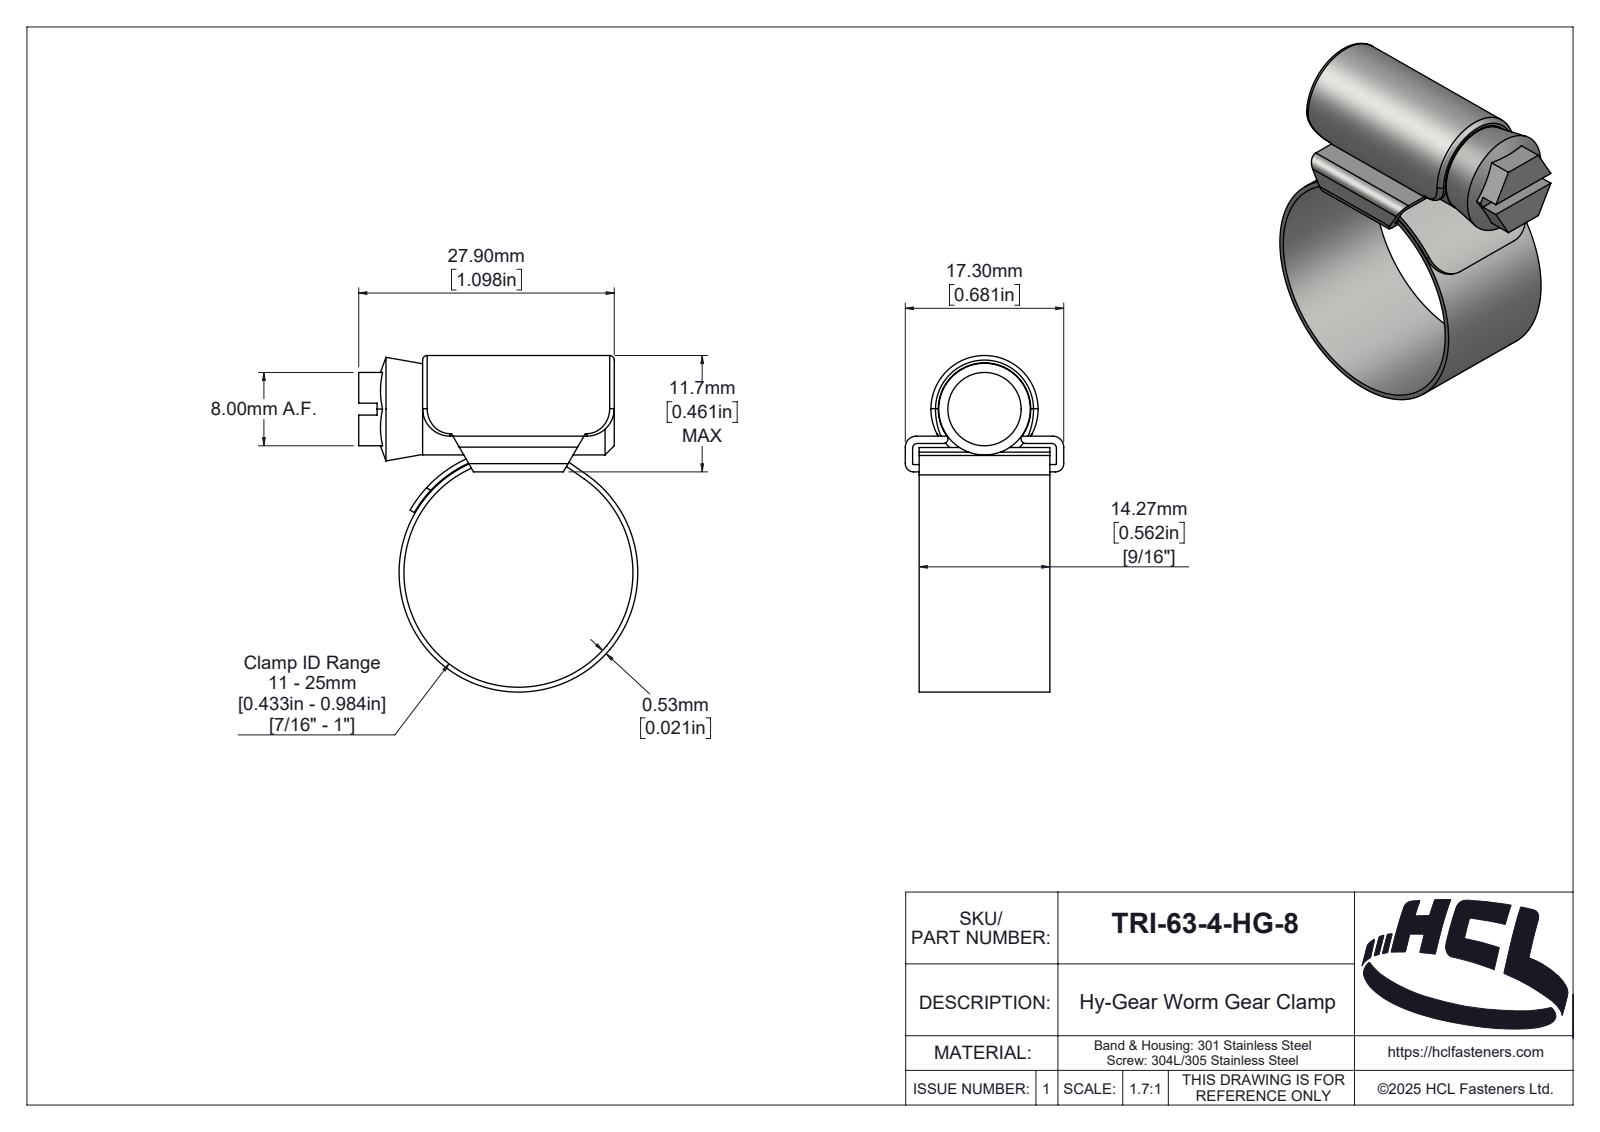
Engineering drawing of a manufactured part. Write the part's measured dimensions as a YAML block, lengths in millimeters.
part_name: "TRI-50-0-HG-8"
step_written_by: "SolidWorks 2025 (AUTOMOTIVE_DESIGN)"
units: millimeters
bodies: {solids: 3, faces: 189, planar: 39, cylindrical: 89, other: 61}
overall_size: [36.73, 30.47, 17.3]
volume: 3505
surface_area: 5598
round_holes:
  - {diameter: 25, count: 1}
round_bosses_or_shafts:
  - {diameter: 26.06, count: 1}
  - {diameter: 10, count: 1}
partial_cylinders:
  - {radius: 0.5, count: 6}
  - {radius: 3, count: 4}
  - {radius: 0.1, count: 2}
  - {radius: 0.9, count: 2}
  - {radius: 1.2, count: 2}
  - {radius: 0.46, count: 1}
  - {radius: 1.89, count: 1}
  - {radius: 2, count: 1}
face_to_face_distances: [0.8, 3.1, 2.3, 3.9, 0.53, 14.26, 27.9, 1.52, 15.78, 16.5]
